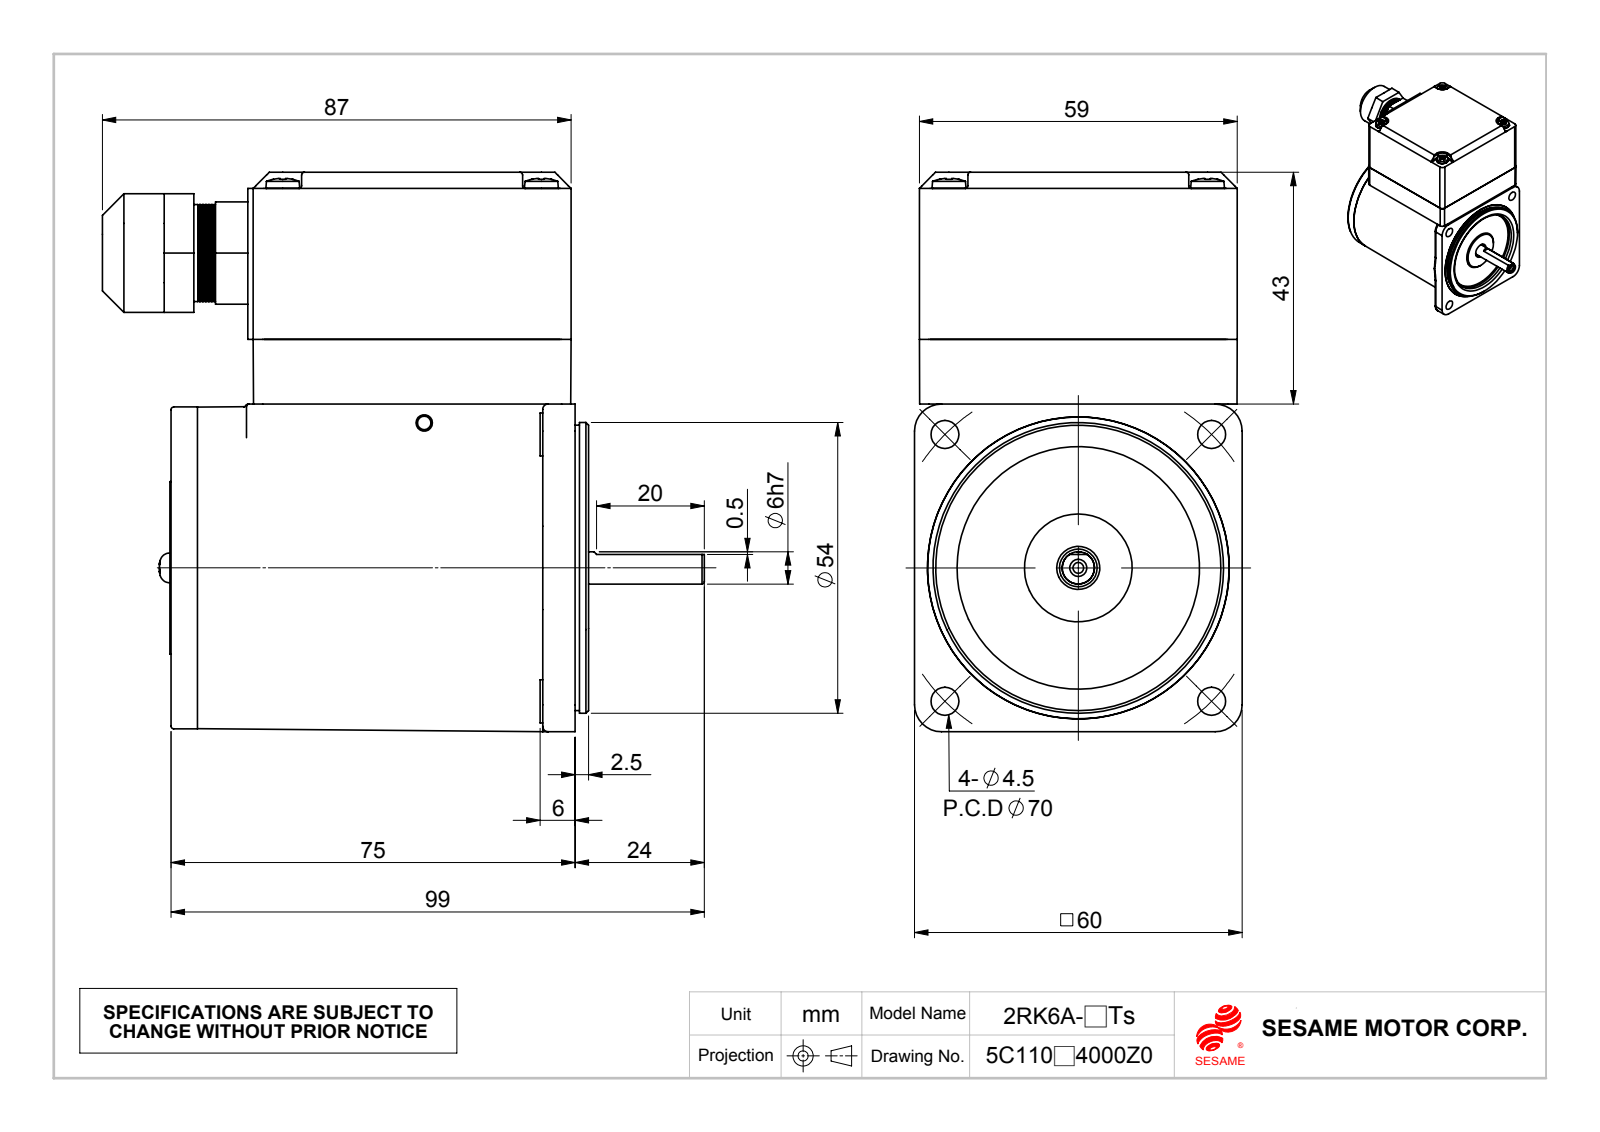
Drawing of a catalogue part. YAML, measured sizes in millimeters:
part_name: "成品180度; 펥짰웰찿M2즤32x1t_Default; M206Ts-RK_2.成品; C254_Default (+2 more)"
step_written_by: "SolidWorks 2010 (CONFIG_CONTROL_DESIGN)"
units: millimeters
bodies: {solids: 14, faces: 2520, planar: 241, cylindrical: 856, other: 1423}
overall_size: [111.75, 103.8, 60.8]
volume: 218754
surface_area: 79314
round_holes:
  - {diameter: 3.2, count: 4}
  - {diameter: 3.3, count: 4}
  - {diameter: 3.5, count: 4}
  - {diameter: 3.9, count: 4}
  - {diameter: 4.3, count: 4}
  - {diameter: 5.2, count: 4}
  - {diameter: 2.5, count: 3}
  - {diameter: 4, count: 2}
  - {diameter: 2, count: 1}
  - {diameter: 7, count: 1}
  - {diameter: 11, count: 1}
  - {diameter: 12, count: 1}
round_bosses_or_shafts:
  - {diameter: 3, count: 6}
  - {diameter: 8, count: 4}
  - {diameter: 6.3, count: 4}
  - {diameter: 5.5, count: 2}
  - {diameter: 59.7, count: 1}
  - {diameter: 53.93, count: 1}
  - {diameter: 52.93, count: 1}
  - {diameter: 32, count: 1}
partial_cylinders:
  - {radius: 0.5, count: 13}
  - {radius: 2, count: 12}
  - {radius: 0.3, count: 8}
  - {radius: 4, count: 6}
  - {radius: 1, count: 4}
  - {radius: 1.5, count: 4}
  - {radius: 3, count: 4}
  - {radius: 3.5, count: 4}
face_to_face_distances: [12, 0.75, 1, 43, 31, 1.5, 59, 73.7, 0.8, 5]
hole_center_spacings: [37.08, 12.25, 9.37, 17.32, 22.63, 22.75, 27.73, 35]
